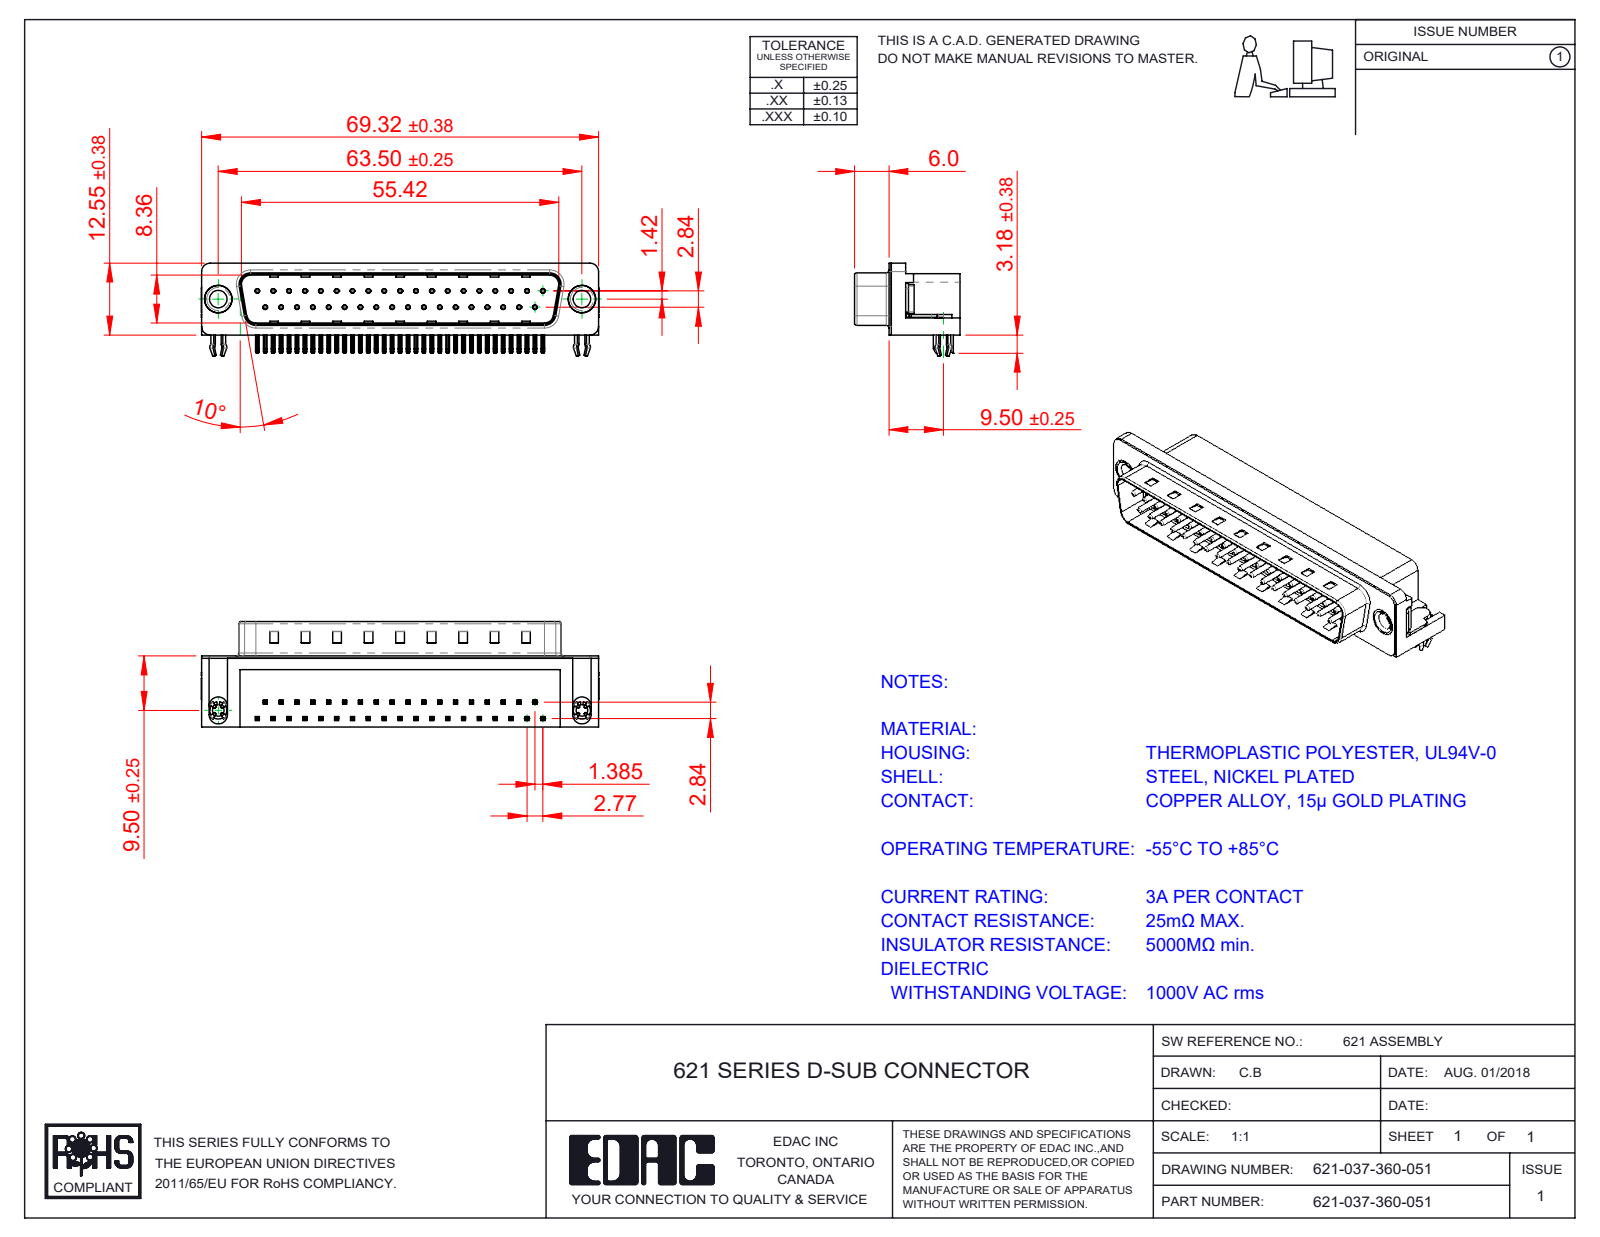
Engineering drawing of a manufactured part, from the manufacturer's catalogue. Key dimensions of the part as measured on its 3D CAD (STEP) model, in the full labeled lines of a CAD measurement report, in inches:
Part name (STEP PRODUCT): 621 4-40 Threaded Board Mount; 621 Contact Top; 621 Contact Bottom; 621 Shell_37 Socket (+3 more)
STEP written by: SolidWorks 2016 (CONFIG_CONTROL_DESIGN)
Units: inches
Bodies: 43 solids, 3189 faces (2013 planar, 909 cylindrical, 267 other)
Overall size (bounding box): 2.732 × 0.724 × 0.619
Volume: 0.526 in³ · Surface area: 15.73 in²
Round holes (diameter × count): ⌀0.014 ×37, ⌀0.031 ×37, ⌀0.089 ×2, ⌀0.12 ×2, ⌀0.157 ×2, ⌀0.189 ×2, ⌀0.197 ×2
Round bosses / shafts (diameter × count): ⌀0.03 ×37, ⌀0.193 ×2, ⌀0.187 ×2, ⌀0.152 ×2, ⌀0.128 ×2
Partial cylindrical surfaces — rounded edges, fillets, slot ends (radius × count): R0.01 ×156, R0.005 ×74, R0.039 ×16, R0.02 ×9, R0.063 ×8, R0.059 ×7, R0.035 ×4, R0.079 ×4
Main face-to-face distances: 0.016, 0.472, 0.407, 0.345, 0.083, 0.067, 0.412, 0.428, 0.354, 0.488
Hole centre spacings: 0.124, 0.109, 0.218, 0.327, 0.436, 0.545, 0.763, 0.872
